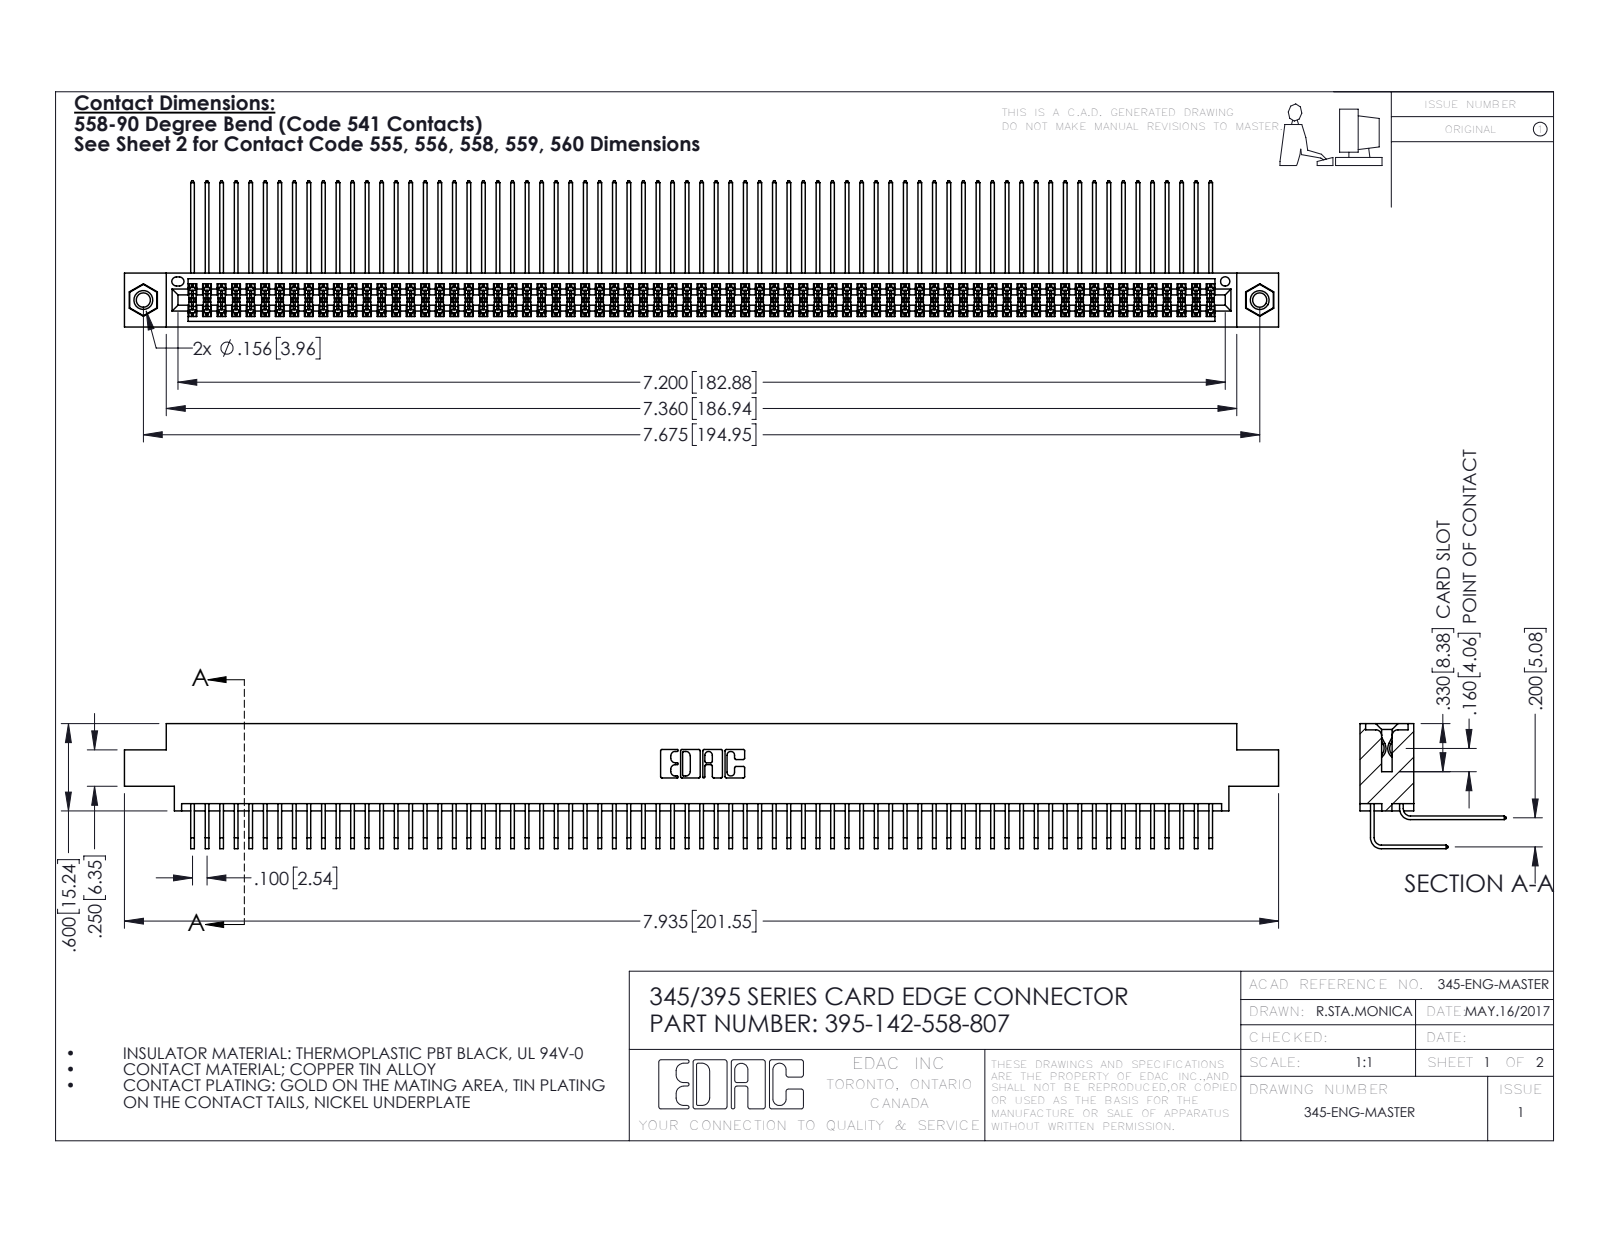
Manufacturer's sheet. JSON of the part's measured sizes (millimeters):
{"part_name": "345-292-001_558 Tail - 2; 395-142-558-807; 345-250-001_345-250-005-103; 345 Part_0.170 Offset - 0.156 Dia-TI (+1 more)", "step_written_by": "SolidWorks 2016 (CONFIG_CONTROL_DESIGN)", "units": "millimeters", "bodies": {"solids": 145, "faces": 7574, "planar": 5086, "cylindrical": 2472, "other": 16}, "overall_size": [201.5, 25.5, 21.8], "volume_mm3": 20530, "surface_area_mm2": 34950, "round_holes": [[2.5, 2], [3.2, 2], [4, 2], [1.6, 1]], "round_bosses_or_shafts": [[3.9, 2]], "partial_cylinders_radius": [[0.2, 283], [0.3, 22], [0.2, 6], [0.8, 6], [0.7, 3], [0.4, 2], [0.5, 2], [0.6, 2]], "face_to_face_distances": [1.8, 7.6, 5.1, 9.4, 2.5, 6.9, 0.6, 5.7, 4.4, 0.6], "hole_center_spacings": [6.9, 189, 194.9]}
